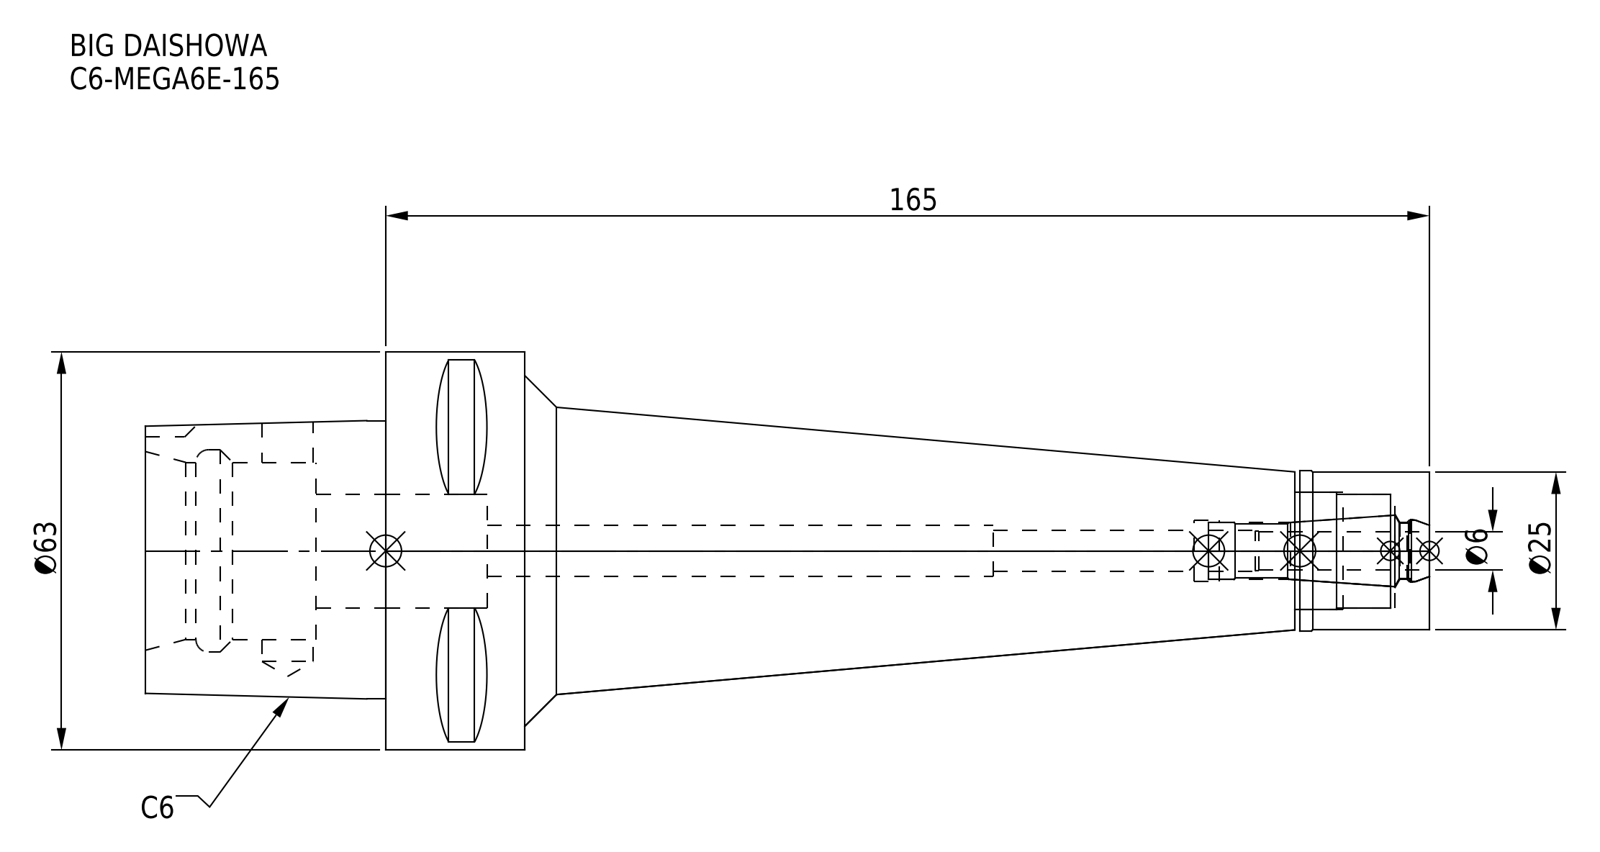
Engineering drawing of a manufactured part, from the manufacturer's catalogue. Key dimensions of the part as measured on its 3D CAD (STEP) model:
Part name (STEP PRODUCT): DXF_TEMP_ASSY_ASM_4_ASM.stp; MEN6_1.stp; C6-MEGA6E-165-060_ASM.stp; C6-MEGA6E-165 (+3 more)
STEP written by: SolidWorks 2019 (CONFIG_CONTROL_DESIGN)
Units: millimetres
Bodies: 2 solids, 100 faces (37 planar, 39 cylindrical, 24 other)
Overall size (bounding box): 203 × 63 × 63
Volume: 225 829 mm³ · Surface area: 40 177 mm²
Round holes (diameter × count): ⌀6.4 ×1, ⌀8 ×1, ⌀8.1 ×1, ⌀9 ×1, ⌀9.6 ×1, ⌀9.9 ×1, ⌀18 ×1, ⌀18.5 ×1, ⌀28 ×1, ⌀32 ×1
Round bosses / shafts (diameter × count): ⌀63 ×1, ⌀25.3 ×1, ⌀25 ×1
Partial cylindrical surfaces — rounded edges, fillets, slot ends (radius × count): R5 ×1
Main face-to-face distances: 22, 27, 60, 38, 143, 165, 203, 176, 33, 11
